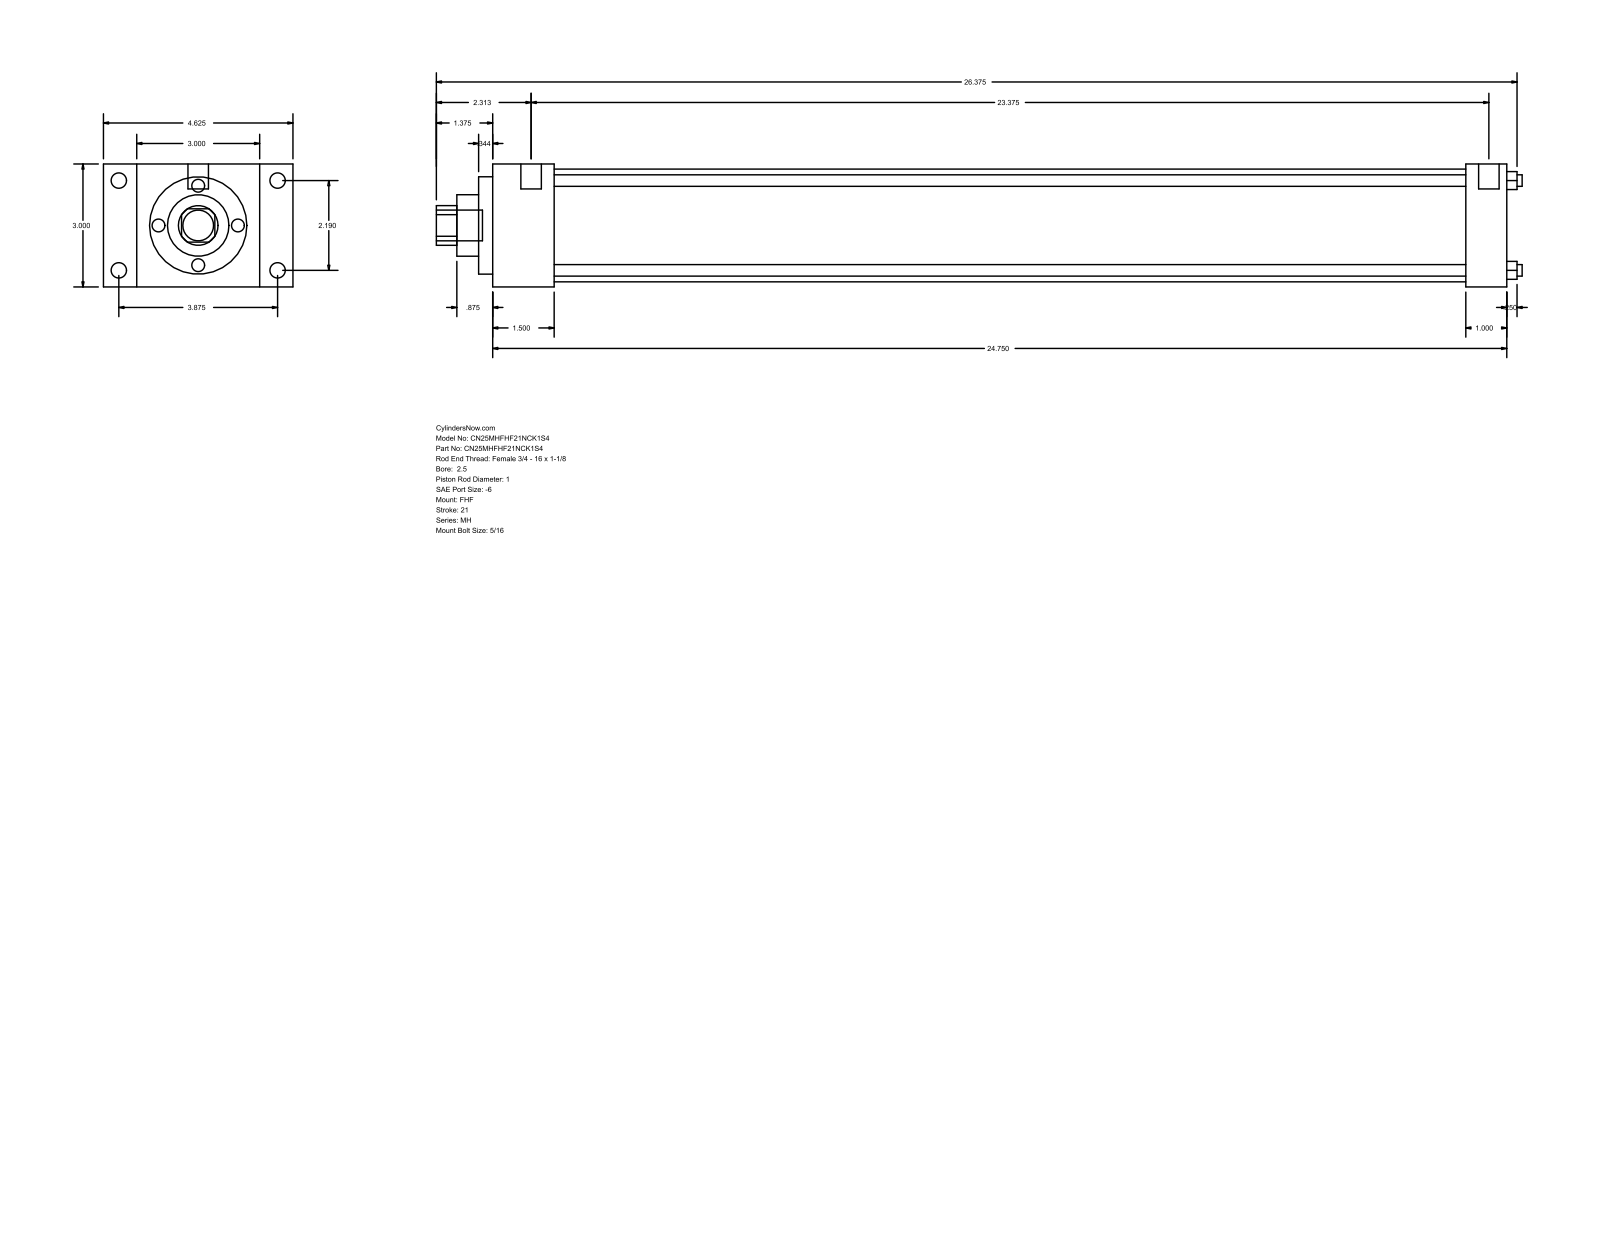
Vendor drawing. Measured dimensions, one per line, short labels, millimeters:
name: MH_FHF__0250_1
written by: GSSL Pune (CONFIG_CONTROL_DESIGN)
unit: mm
bodies: 0 solids, 90 faces (61 planar, 29 cylindrical, 0 other)
size: 673.1 × 117.47 × 76.2
holes: 4× ⌀7.14, 1× ⌀25.4, 1× ⌀38.1, 1× ⌀60.33, 1× ⌀69.85
bosses: 4× ⌀9.53, 4× ⌀5.56, 2× ⌀12.7, 1× ⌀19.05
rounds: 1× R12.29
face distances: 76.2, 628.66, 38.11, 590.55, 20.64, 96.84, 117.48, 603.25, 565.14, 25.41
hole spacings: 39.33, 55.62, 78.66
